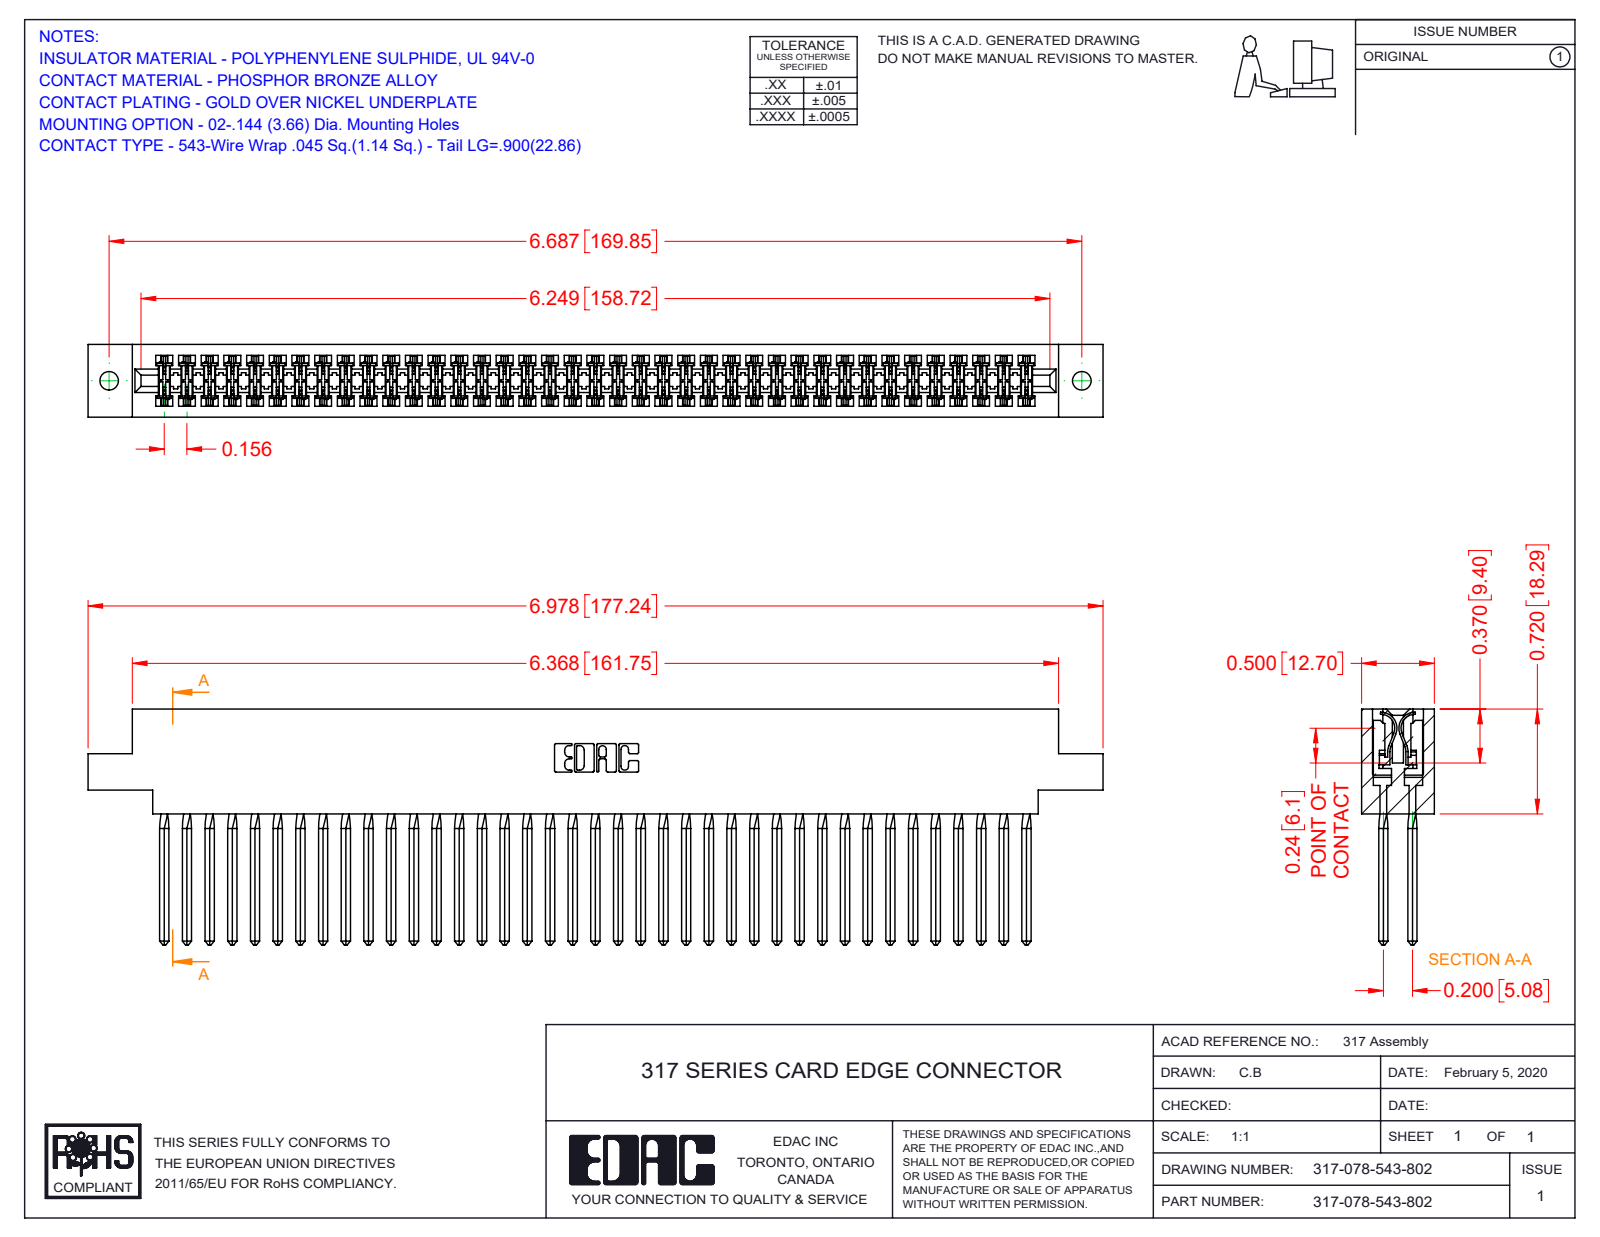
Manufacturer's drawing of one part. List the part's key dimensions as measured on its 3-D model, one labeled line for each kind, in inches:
Part name (STEP PRODUCT): 317 Part_.144 Dia; 317-078-543-802; 317-290-001_543
STEP written by: SolidWorks 2016 (CONFIG_CONTROL_DESIGN)
Units: inches
Bodies: 79 solids, 7044 faces (5752 planar, 980 cylindrical, 312 other)
Overall size (bounding box): 6.978 × 1.62 × 0.5
Volume: 1.831 in³ · Surface area: 69.94 in²
Round holes (diameter × count): ⌀0.128 ×2
Partial cylindrical surfaces — rounded edges, fillets, slot ends (radius × count): R0.015 ×156, R0.01 ×22, R0.007 ×6, R0.031 ×6, R0.026 ×3, R0.095 ×2, R0.1 ×2, R0.11 ×2
Main face-to-face distances: 0.5, 0.075, 0.425, 0.35, 0.11, 0.195, 0.094, 0.2, 0.115, 0.131
Hole centre spacings: 6.687
